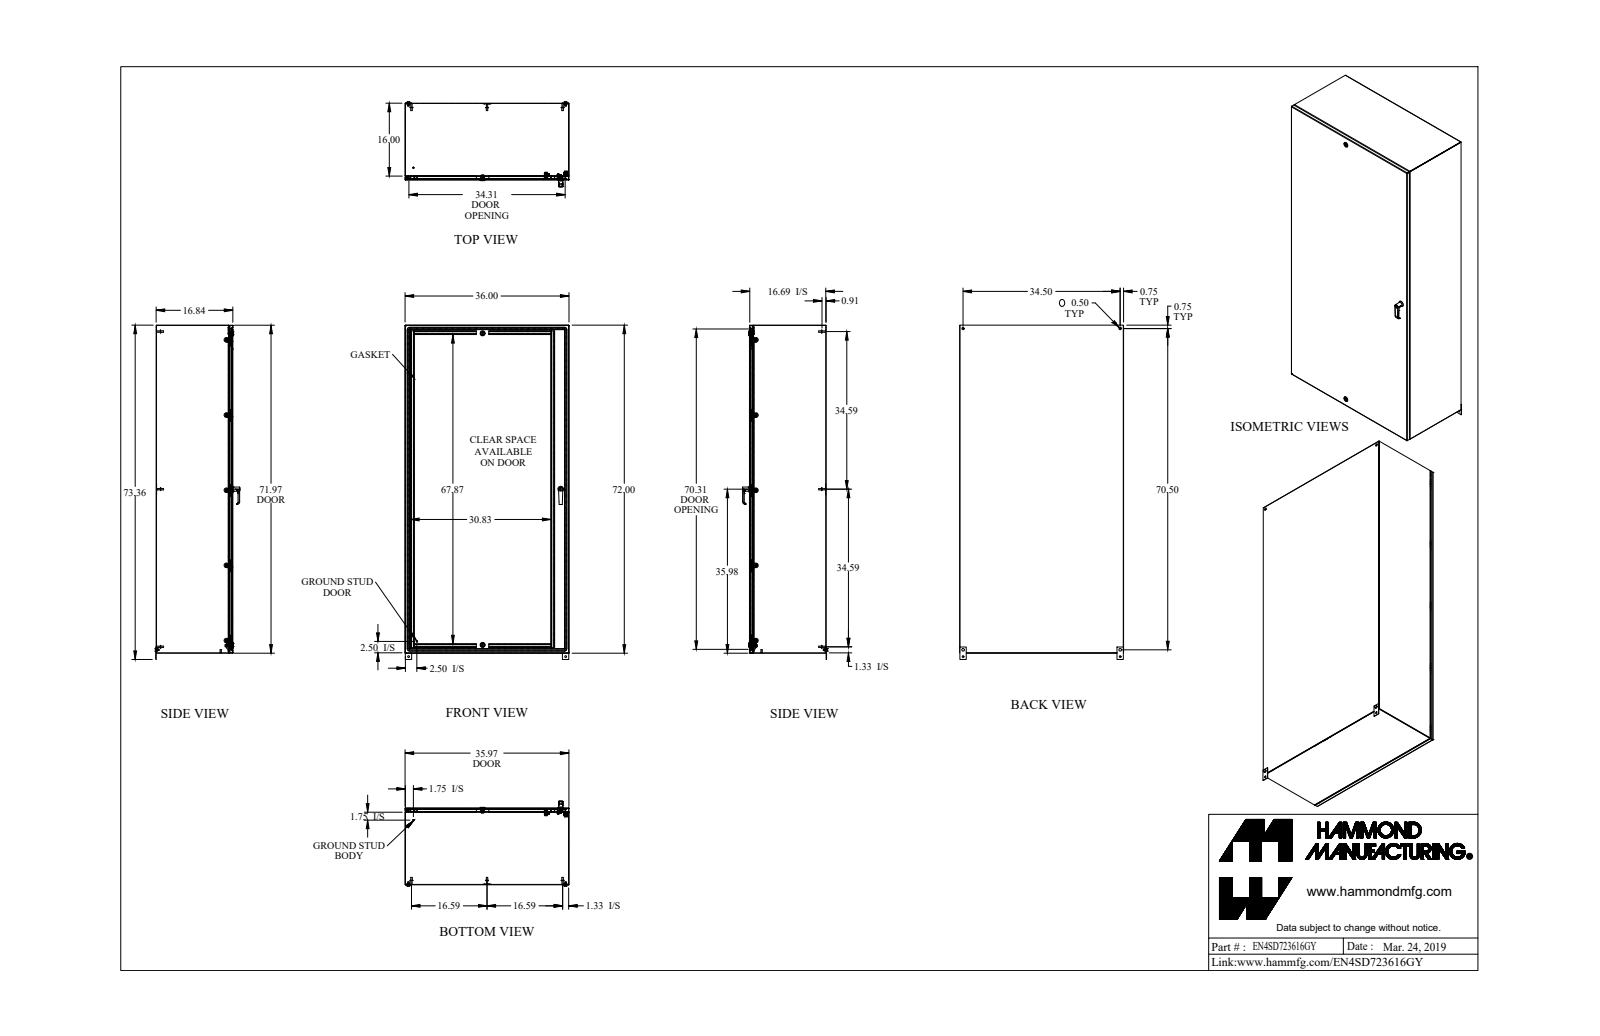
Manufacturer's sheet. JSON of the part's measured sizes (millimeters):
{"part_name": "EN4SD723616GY", "step_written_by": "SolidWorks 2018 (AUTOMOTIVE_DESIGN)", "units": "millimeters", "bodies": {"solids": 100, "faces": 2461, "planar": 1167, "cylindrical": 902, "other": 392}, "overall_size": [1863.4, 914.4, 474.8], "volume_mm3": 11680000, "surface_area_mm2": 12910000, "round_holes": [[4.5, 10], [5, 6], [6.4, 5], [6.7, 5], [10.5, 5], [6.5, 4], [8, 4], [9.9, 4], [10, 4], [12.7, 4], [5.9, 2], [7.8, 2]], "round_bosses_or_shafts": [[6.4, 11], [9.5, 10], [4, 10], [15.9, 9], [8, 8], [6.9, 8], [25.4, 5], [16, 4]], "partial_cylinders_radius": [[1.1, 24], [1.6, 19], [0.9, 17], [2.7, 17], [0.8, 15], [3.2, 14], [0.2, 10], [2.4, 10]], "face_to_face_distances": [1.8, 425.8, 424, 427.7, 912.6, 910.7, 914.4, 1827, 1825.1, 1828.8], "hole_center_spacings": [419.4, 876.3, 1257, 38.1, 63.7, 414.1, 418.8, 419.1]}
